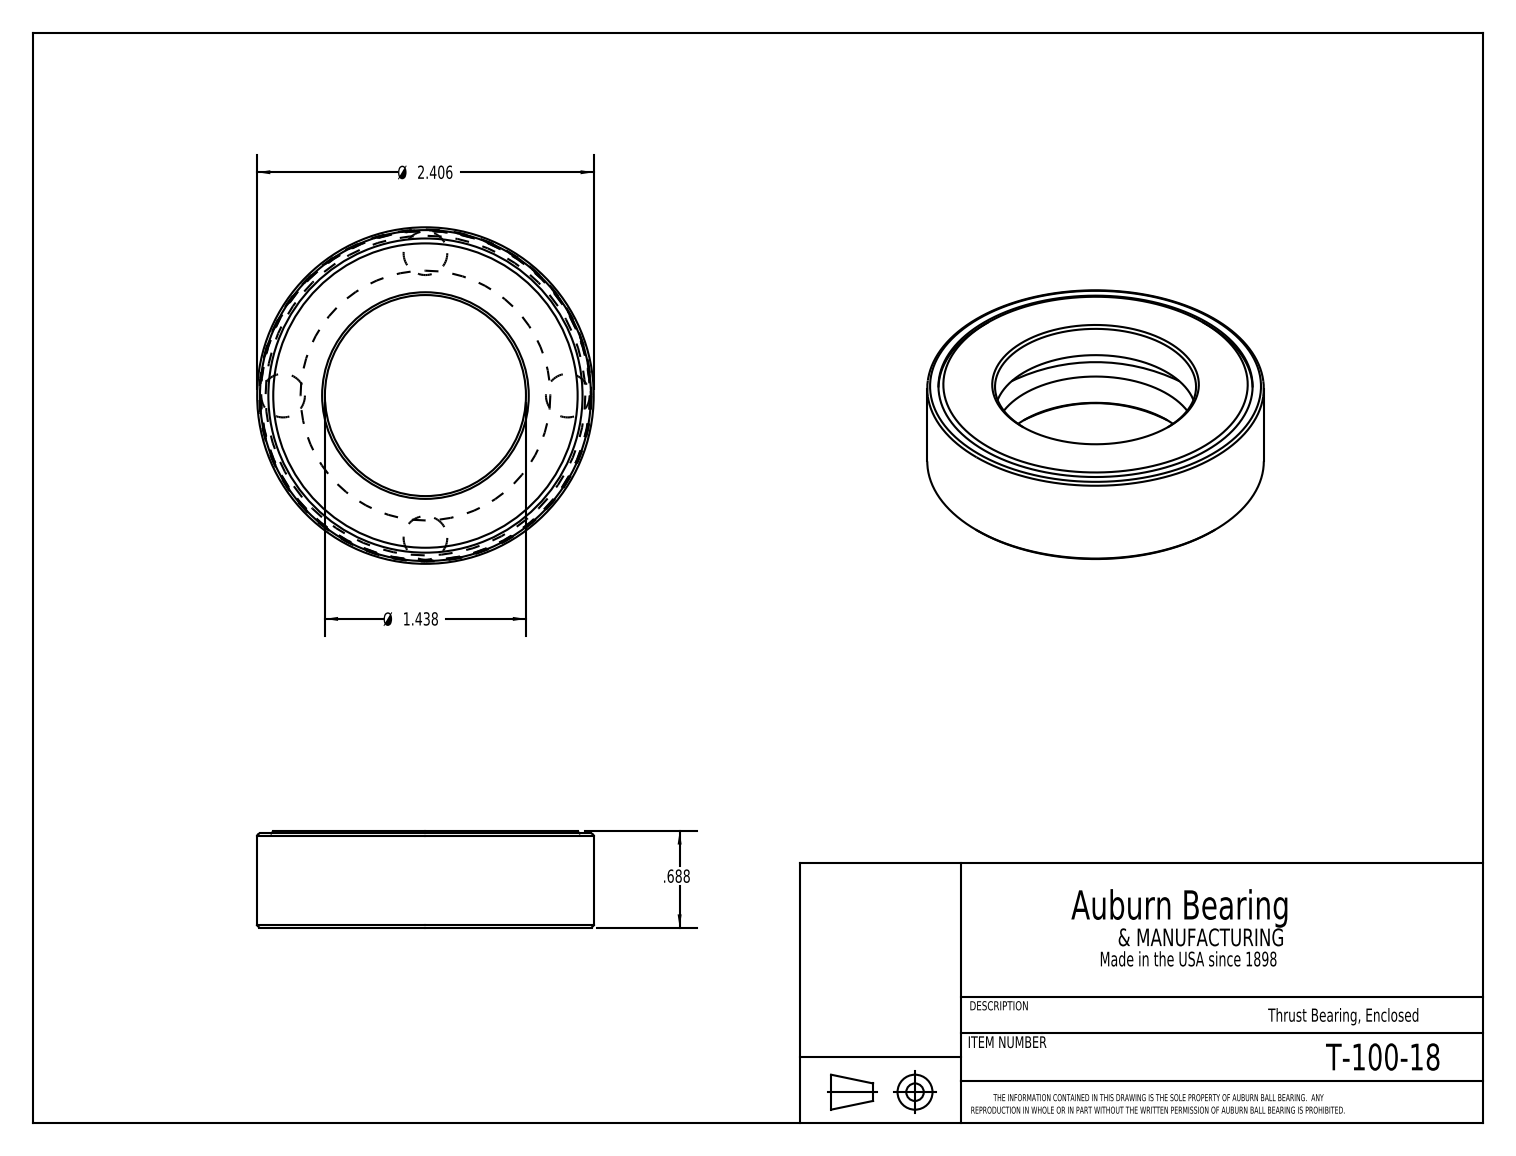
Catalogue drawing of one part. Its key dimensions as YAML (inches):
part_name: "T-100-18"
step_written_by: "SolidWorks 2016 (CONFIG_CONTROL_DESIGN)"
units: inches
bodies: {solids: 6, faces: 28, planar: 9, cylindrical: 7, other: 12}
overall_size: [2.406, 2.406, 0.688]
volume: 1.377
surface_area: 25.65
round_holes:
  - {diameter: 1.437, count: 1}
  - {diameter: 2.246, count: 1}
  - {diameter: 2.366, count: 1}
round_bosses_or_shafts:
  - {diameter: 2.406, count: 1}
  - {diameter: 2.352, count: 1}
face_to_face_distances: [0.25, 0.437, 0.687, 0.187, 0.652, 0.672, 0.402, 0.422, 0.215, 0.235]
